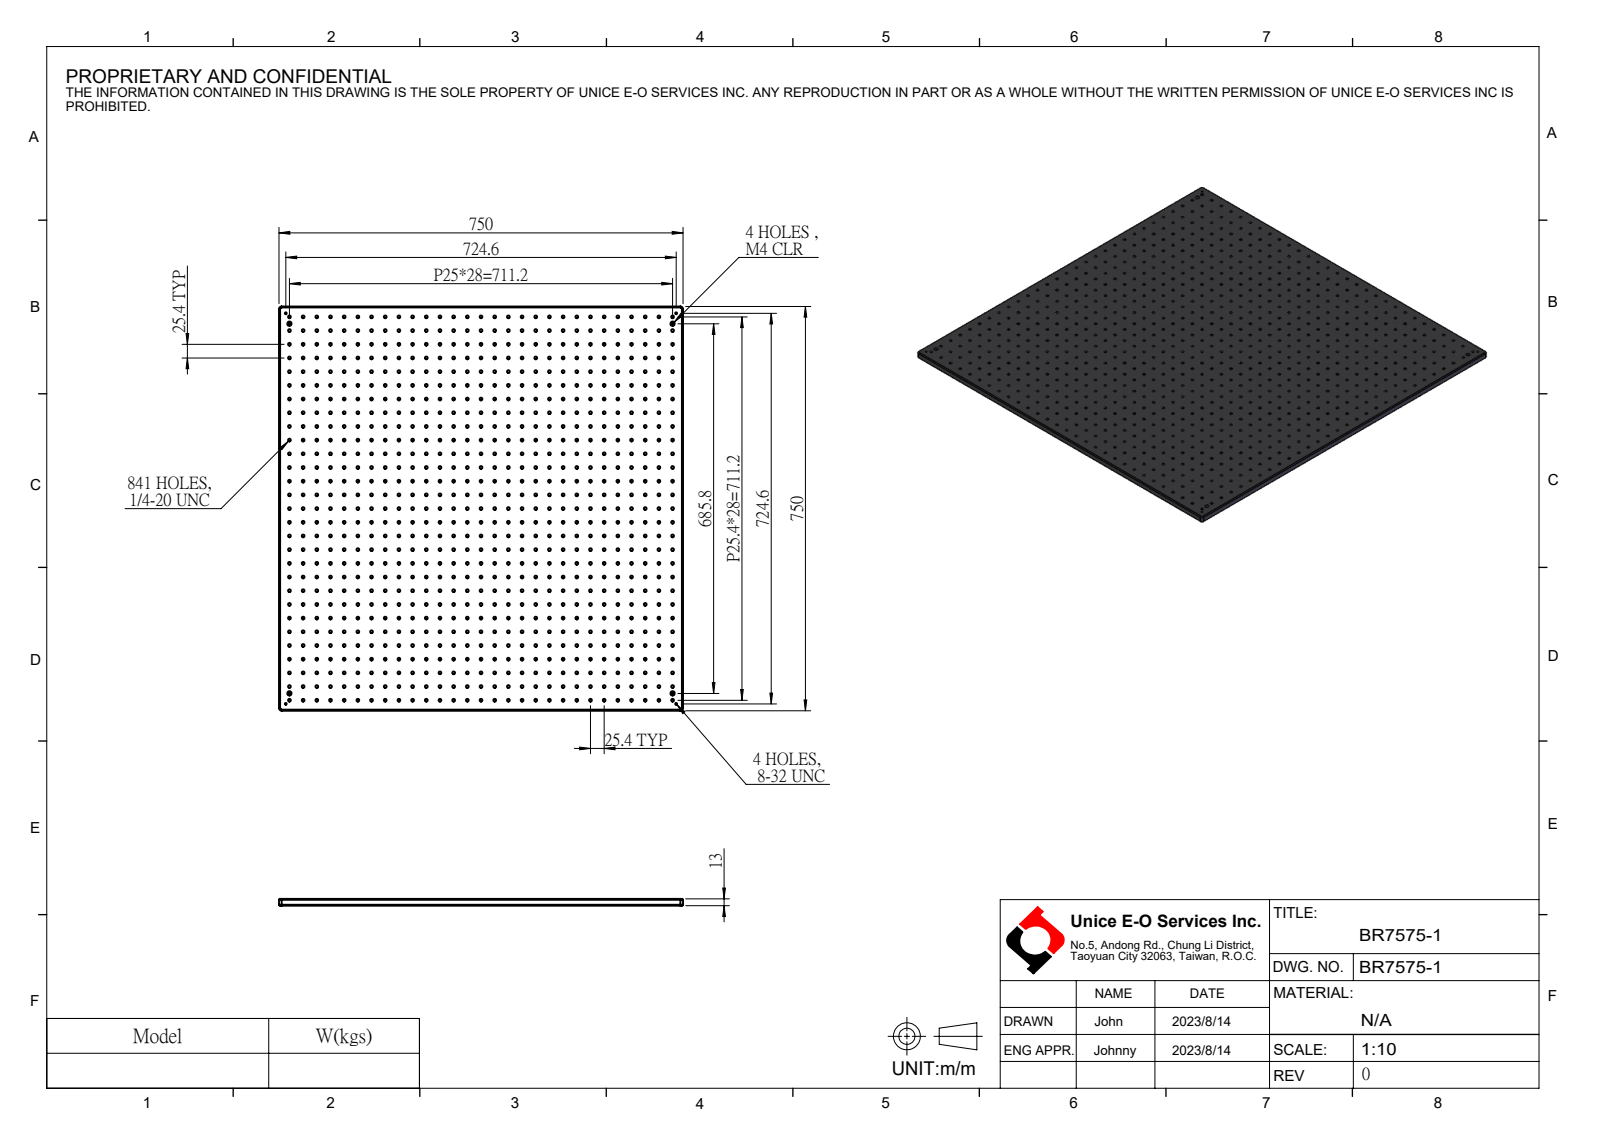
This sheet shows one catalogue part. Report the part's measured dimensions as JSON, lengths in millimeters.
{"part_name": "BR7575-1", "step_written_by": "SolidWorks 2021 (CONFIG_CONTROL_DESIGN)", "units": "millimeters", "bodies": {"solids": 1, "faces": 1736, "planar": 10, "cylindrical": 1718, "other": 8}, "overall_size": [750, 750, 13], "volume_mm3": 7081000, "surface_area_mm2": 1301000, "round_holes": [[5.11, 841], [3.45, 4], [4.5, 4], [8, 4]], "partial_cylinders_radius": [[2, 8], [5, 4]], "face_to_face_distances": [13, 750, 8.6, 4.4], "hole_center_spacings": [25.4, 50.8, 76.2, 101.6, 127, 152.4, 177.8, 203.2]}
